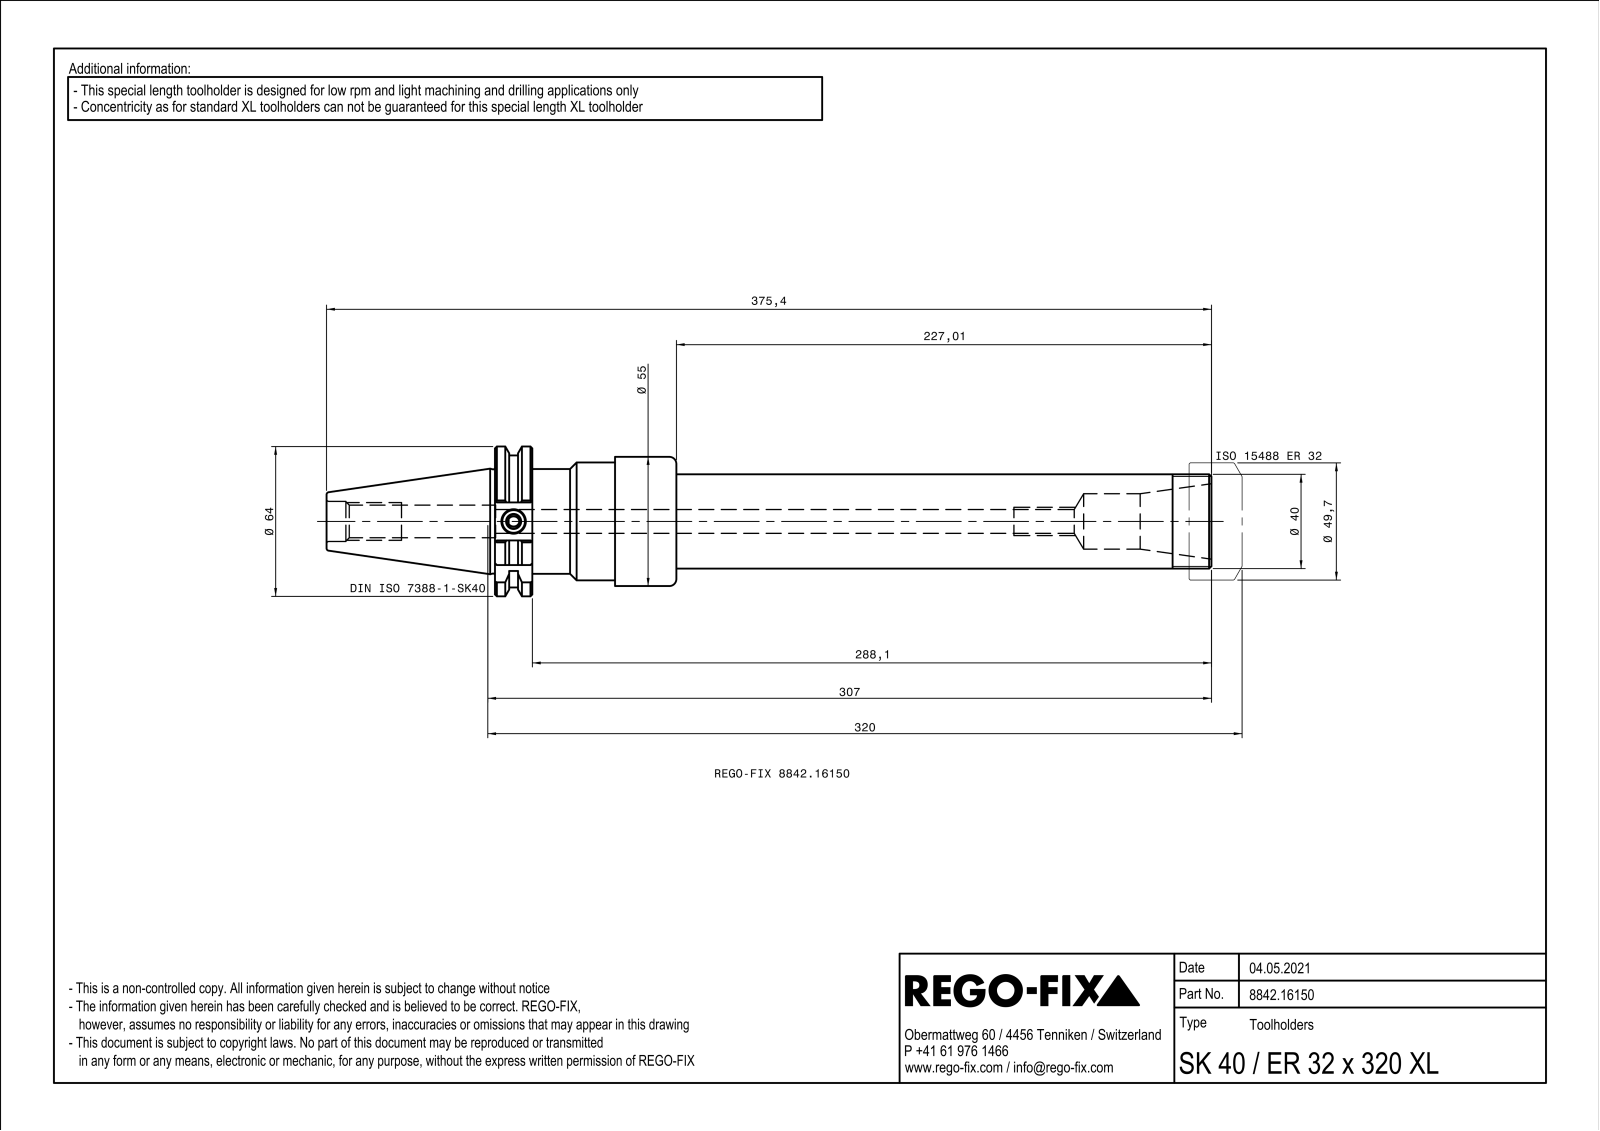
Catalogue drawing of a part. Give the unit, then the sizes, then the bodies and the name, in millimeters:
Units: millimetres
Overall size (bounding box): 375.25 × 63.55 × 61.01
Round holes (diameter × count): ⌀6 ×1, ⌀10 ×1, ⌀10.1 ×1, ⌀10.11 ×1, ⌀13.84 ×1, ⌀17 ×1, ⌀23.5 ×1, ⌀33 ×1, ⌀40.2 ×1, ⌀48.38 ×1, ⌀50.05 ×1, ⌀51.3 ×1
Round bosses / shafts (diameter × count): ⌀54.8 ×1, ⌀50 ×1, ⌀45 ×1, ⌀44.45 ×1, ⌀44.15 ×1, ⌀42 ×1, ⌀40 ×1, ⌀31.6 ×1
Partial cylindrical surfaces — rounded edges, fillets, slot ends (radius × count): R0.5 ×13, R28 ×1, R31.77 ×1
Main face-to-face distances: 15.85, 6.05, 9.8, 60.94, 66.99, 76.79, 7.99, 52.95, 59, 68.8
Volume: 451 028 mm³ · Surface area: 80 793 mm²
Bodies: 1 solid, 156 faces (51 planar, 44 cylindrical, 61 other)
Part name (STEP PRODUCT): NOCUT
STEP written by: SIEMENS PLM Software Solid Edge ST10 (AUTOMOTIVE_DESIGN)
